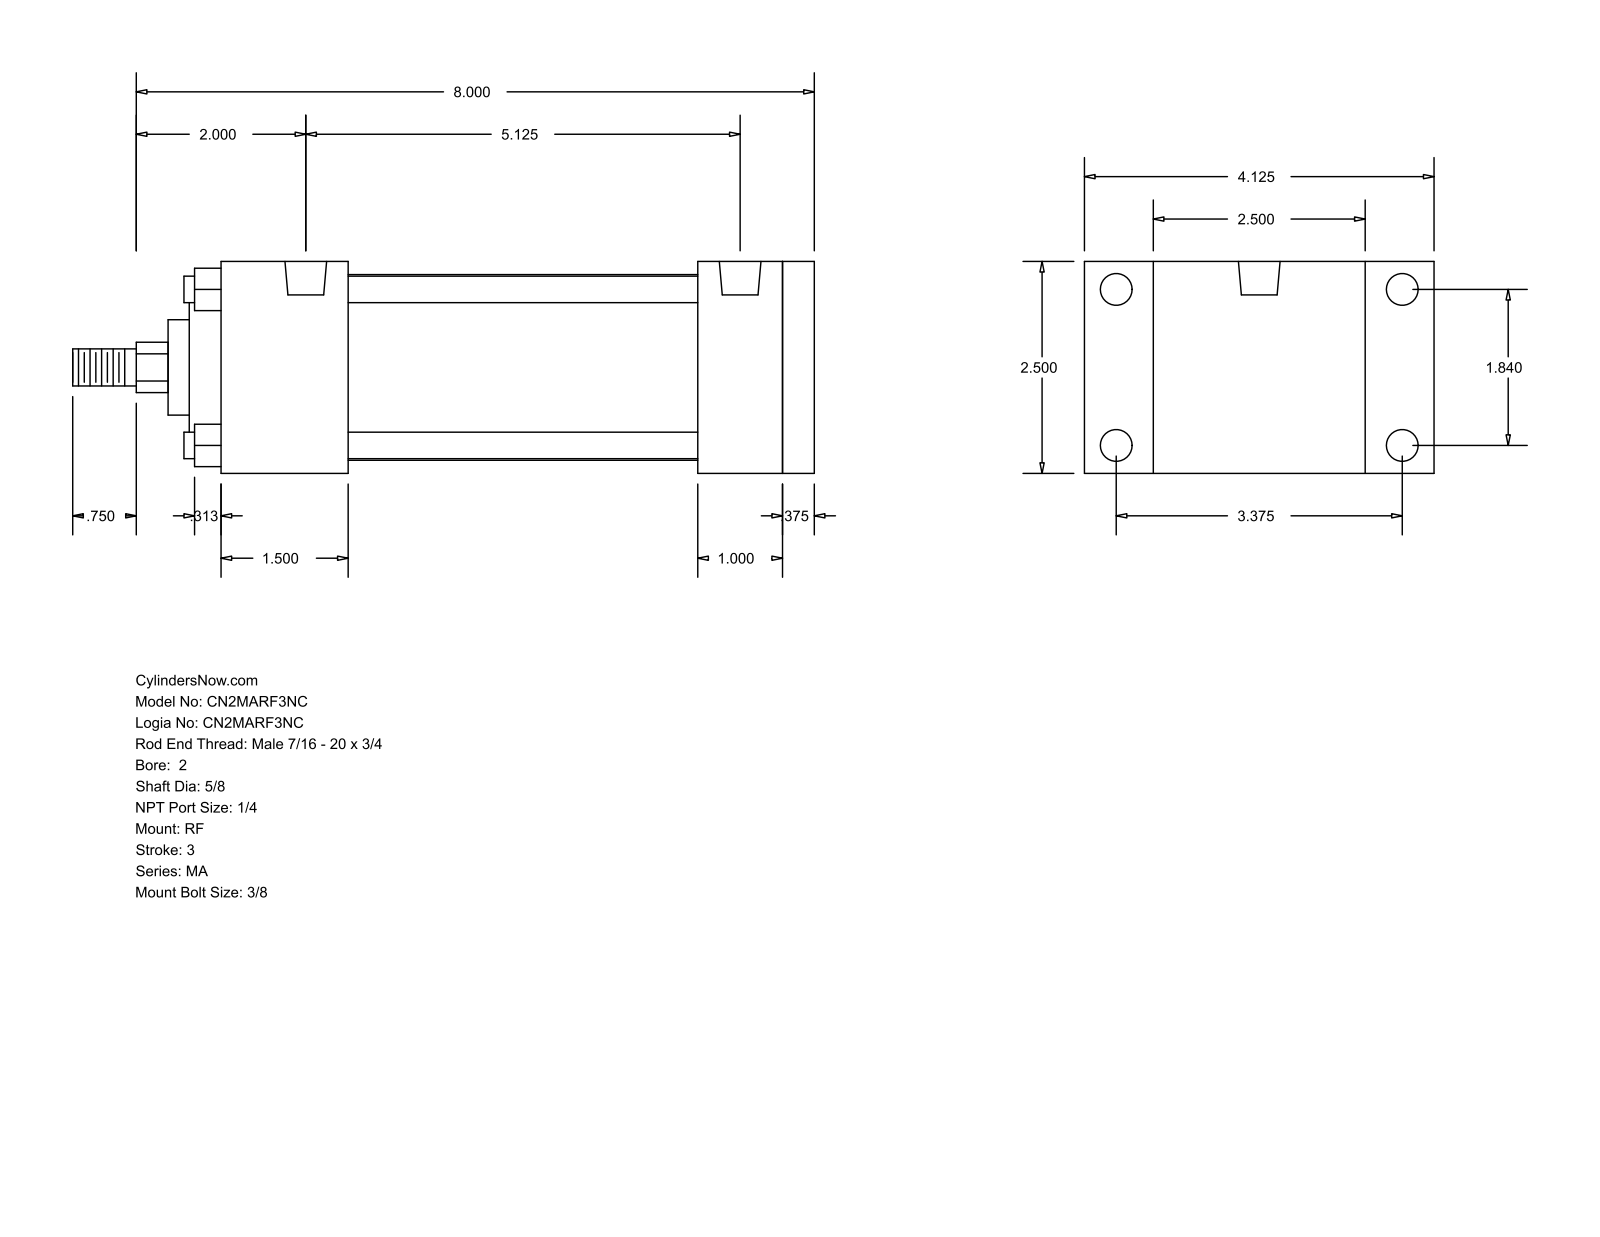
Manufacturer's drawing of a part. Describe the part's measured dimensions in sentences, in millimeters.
The part is named "MA_RF__0200_0.625". Its 3-D file was written by "GSSL Pune (CONFIG_CONTROL_DESIGN)". It is 0 solids with 94 faces: 65 planar, 29 cylindrical and 0 other. Overall it measures 222.25 by 104.78 by 63.5 millimeters. Round holes: 4 of diameter 7.94, 4 of diameter 9.53, 2 of diameter 12.49. Round bosses or shafts: 4 of diameter 7.94, 1 of diameter 55.63, 1 of diameter 50.8, 1 of diameter 28.57, 1 of diameter 15.88, 1 of diameter 11.11. Partial cylindrical surfaces (rounded edges, fillets, slot ends): 1 of radius 7.54. The main face-to-face distances are 63.5, 9.52, 177.8, 104.78, 25.4, 38.1, 168.28, 130.18, 139.7, 142.88. The hole center spacings are 46.74, 85.72, 97.63, 130.17.
